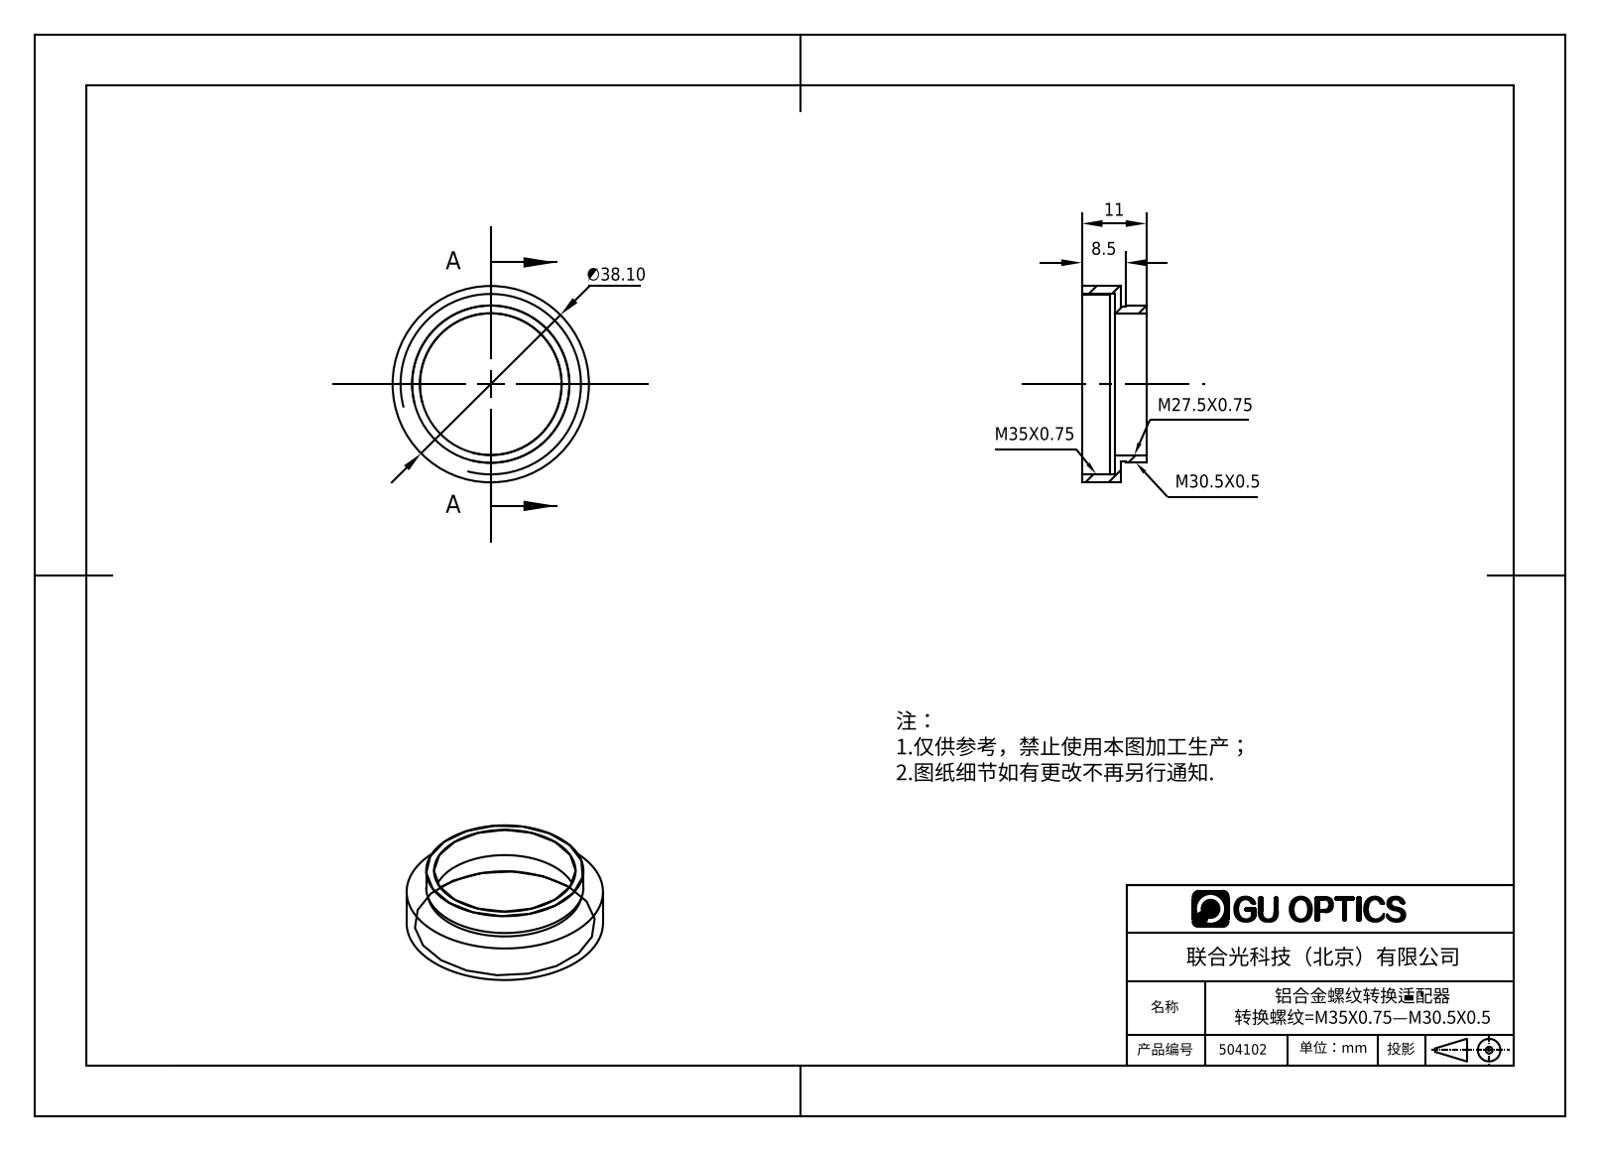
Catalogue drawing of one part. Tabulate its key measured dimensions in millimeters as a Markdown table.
| quantity | value |
| --- | --- |
| part name | 504102 |
| STEP written by | SolidWorks 2016 (AUTOMOTIVE_DESIGN) |
| units | millimeters |
| bodies | 1 solid, 18 faces (6 planar, 12 cylindrical, 0 other) |
| overall size | 38.1 × 38.1 × 11 |
| volume | 2 582 mm³ |
| surface area | 3 474 mm² |
| round holes (diameter × count) | 27.48 × 1, 34.8 × 1, 35 × 1 |
| round bosses / shafts (diameter × count) | 38.1 × 1, 30.52 × 1, 30 × 1 |
| main face-to-face distances | 2, 5.5, 7.5, 11, 3.5, 1, 3, 8.5, 2.5, 4.5 |
